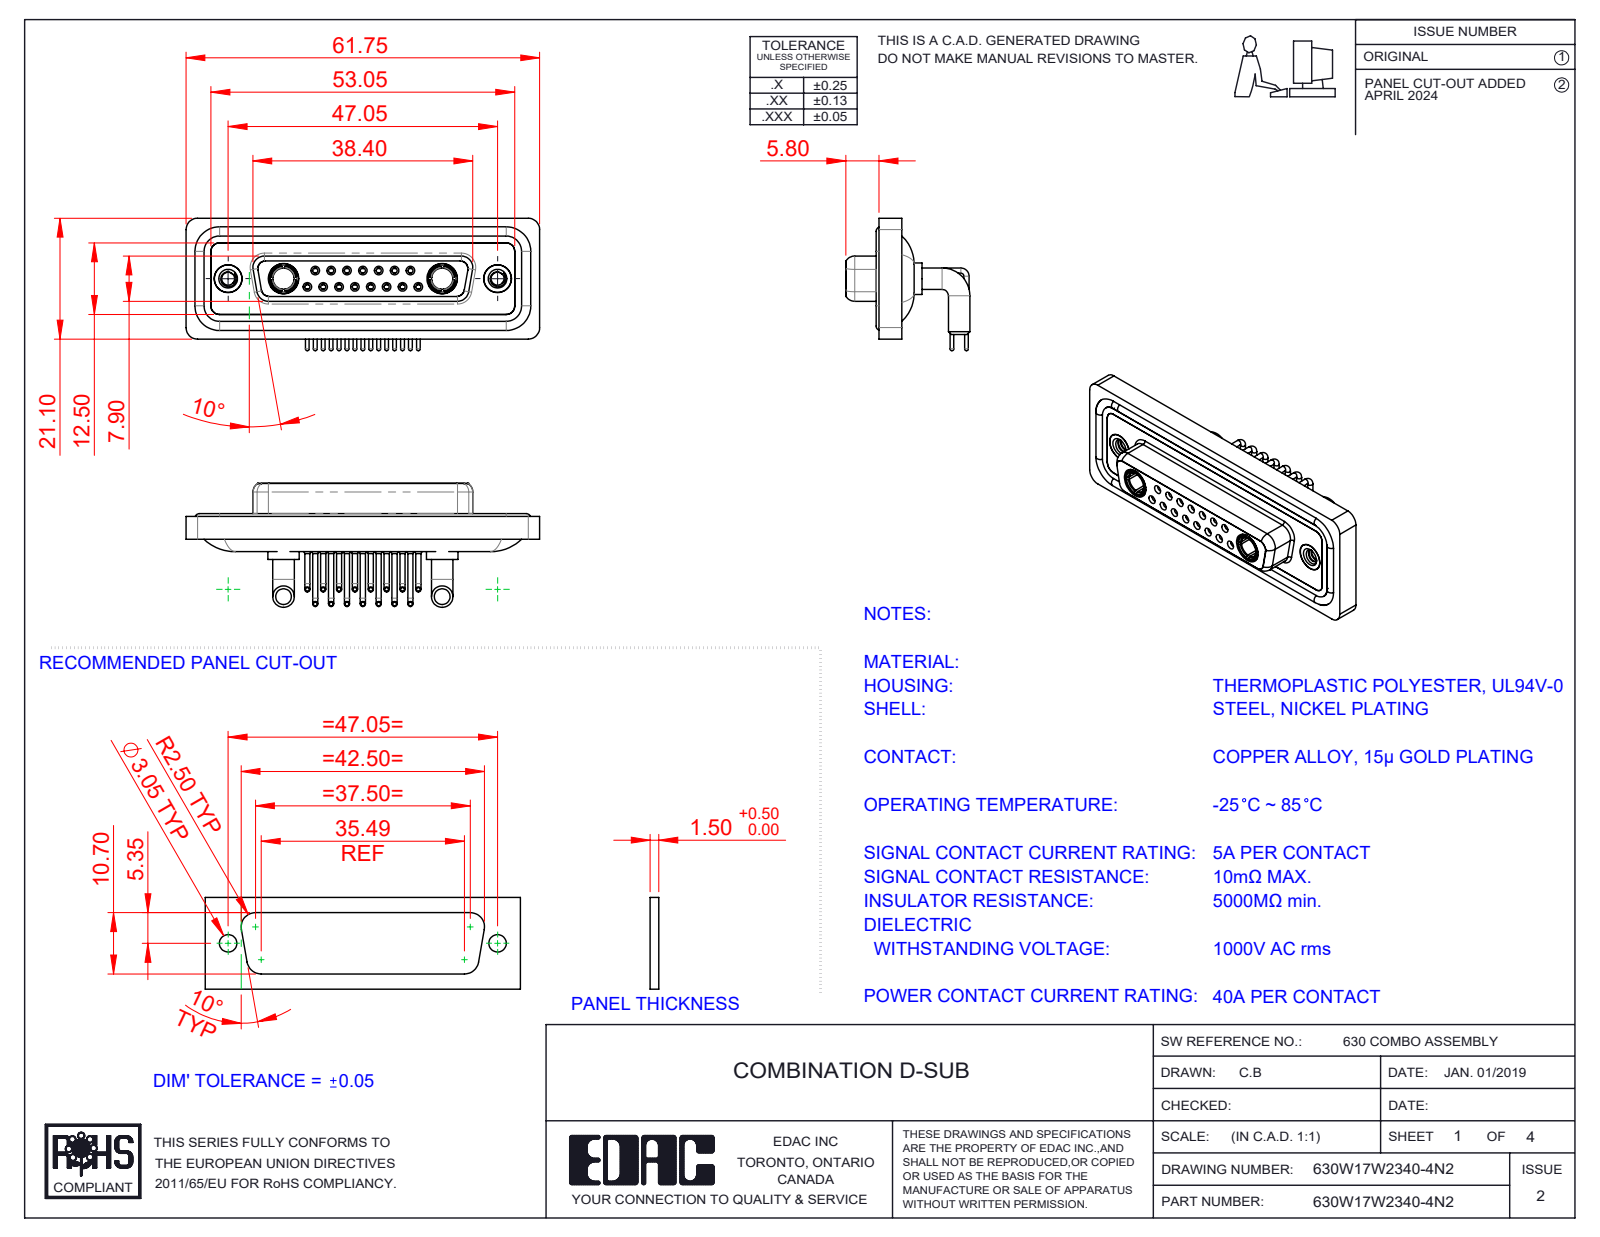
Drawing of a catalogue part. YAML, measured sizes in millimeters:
part_name: "630Combo Contact Row 1_50 Contacts; Power Socket_40A RA; 630Combo Threaded Rivet_2; 630Combo Contact Row 2_50 Contacts (+5 more)"
step_written_by: "SolidWorks 2023 (CONFIG_CONTROL_DESIGN)"
units: millimeters
bodies: {solids: 26, faces: 1337, planar: 388, cylindrical: 583, other: 366}
overall_size: [61.75, 23.12, 21.68]
volume: 8632
surface_area: 14618
round_holes:
  - {diameter: 0.9, count: 15}
  - {diameter: 1.1, count: 15}
  - {diameter: 1.5, count: 15}
  - {diameter: 2, count: 15}
  - {diameter: 1.6, count: 8}
  - {diameter: 1.7, count: 7}
  - {diameter: 4.85, count: 4}
  - {diameter: 2.26, count: 2}
  - {diameter: 3.7, count: 2}
  - {diameter: 4, count: 2}
  - {diameter: 4.05, count: 2}
  - {diameter: 5, count: 2}
round_bosses_or_shafts:
  - {diameter: 0.9, count: 15}
  - {diameter: 0.65, count: 15}
  - {diameter: 1.6, count: 11}
  - {diameter: 3.75, count: 4}
  - {diameter: 5.5, count: 2}
  - {diameter: 5.2, count: 2}
  - {diameter: 4.96, count: 2}
  - {diameter: 4.95, count: 2}
partial_cylinders:
  - {radius: 1.5, count: 18}
  - {radius: 2, count: 18}
  - {radius: 1.35, count: 8}
  - {radius: 1.6, count: 8}
  - {radius: 0.25, count: 4}
  - {radius: 0.5, count: 4}
  - {radius: 0.6, count: 4}
  - {radius: 0.65, count: 4}
face_to_face_distances: [0.4, 1.8, 4.1, 1.1, 1.6, 3.1, 2.5, 1.5, 3.7, 1.4]
hole_center_spacings: [3.16, 2.77, 5.54, 8.31, 5.04, 7.49, 11.08, 5.03]
